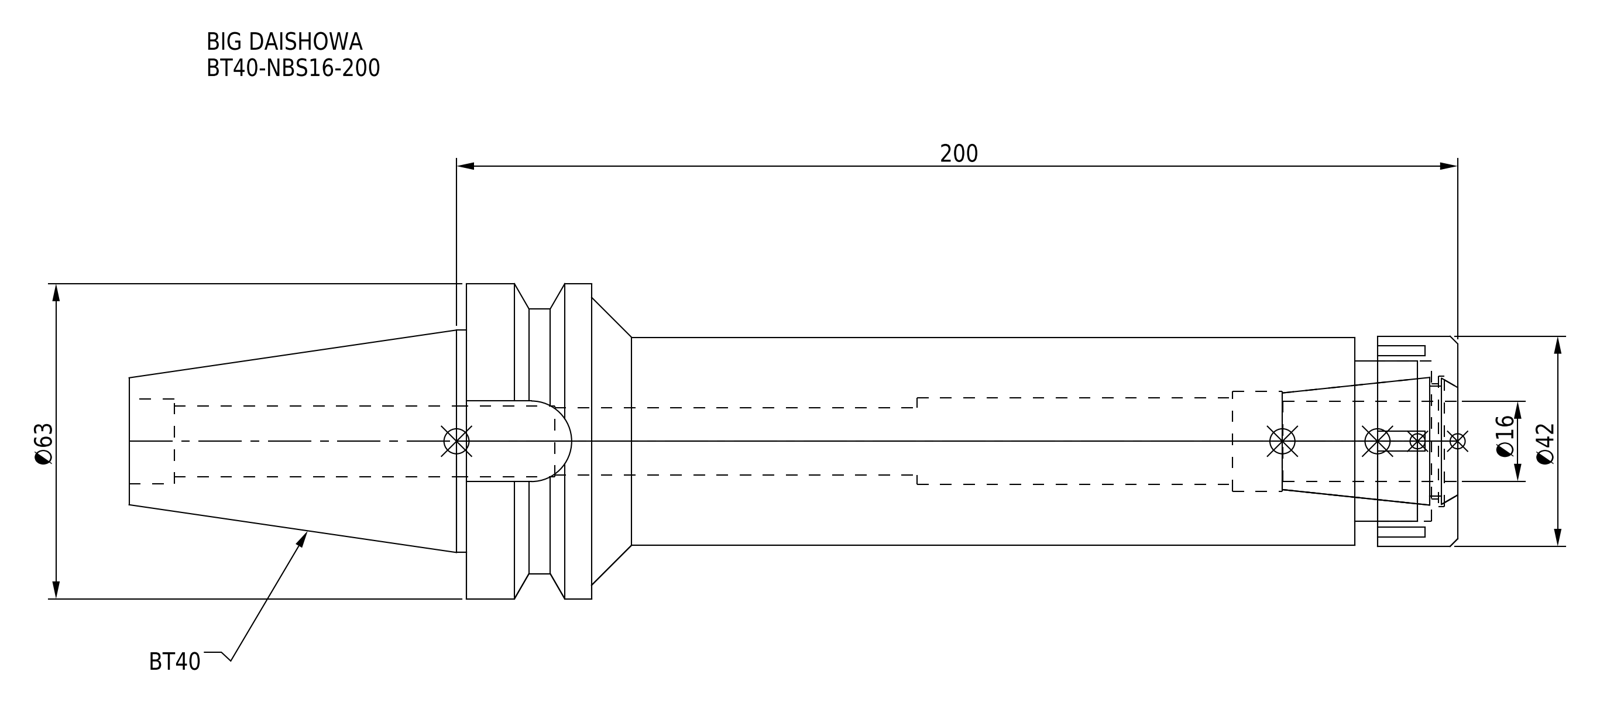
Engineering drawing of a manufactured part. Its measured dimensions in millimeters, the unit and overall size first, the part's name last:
Units: millimetres
Overall size (bounding box): 265.4 × 63 × 63
Round holes (diameter × count): ⌀13.5 ×1, ⌀14.2 ×1, ⌀17 ×1, ⌀17.3 ×1, ⌀20 ×1, ⌀23 ×1, ⌀26 ×1, ⌀32 ×1
Round bosses / shafts (diameter × count): ⌀63 ×1, ⌀53 ×1, ⌀44.45 ×1, ⌀42 ×1, ⌀41.5 ×1
Partial cylindrical surfaces — rounded edges, fillets, slot ends (radius × count): R8.05 ×1
Main face-to-face distances: 198, 8, 20.5, 177.5, 16, 4.5, 182, 173, 157, 152.5
Volume: 312 941 mm³ · Surface area: 57 711 mm²
Bodies: 2 solids, 93 faces (45 planar, 34 cylindrical, 14 other)
Part name (STEP PRODUCT): BT40-NBS16-200.stp; BT40-NBS16-200_1.stp; BT40NB16200-160_ASM.stp; BT40-NBS16-200 (+3 more)
STEP written by: SolidWorks 2019 (CONFIG_CONTROL_DESIGN)
